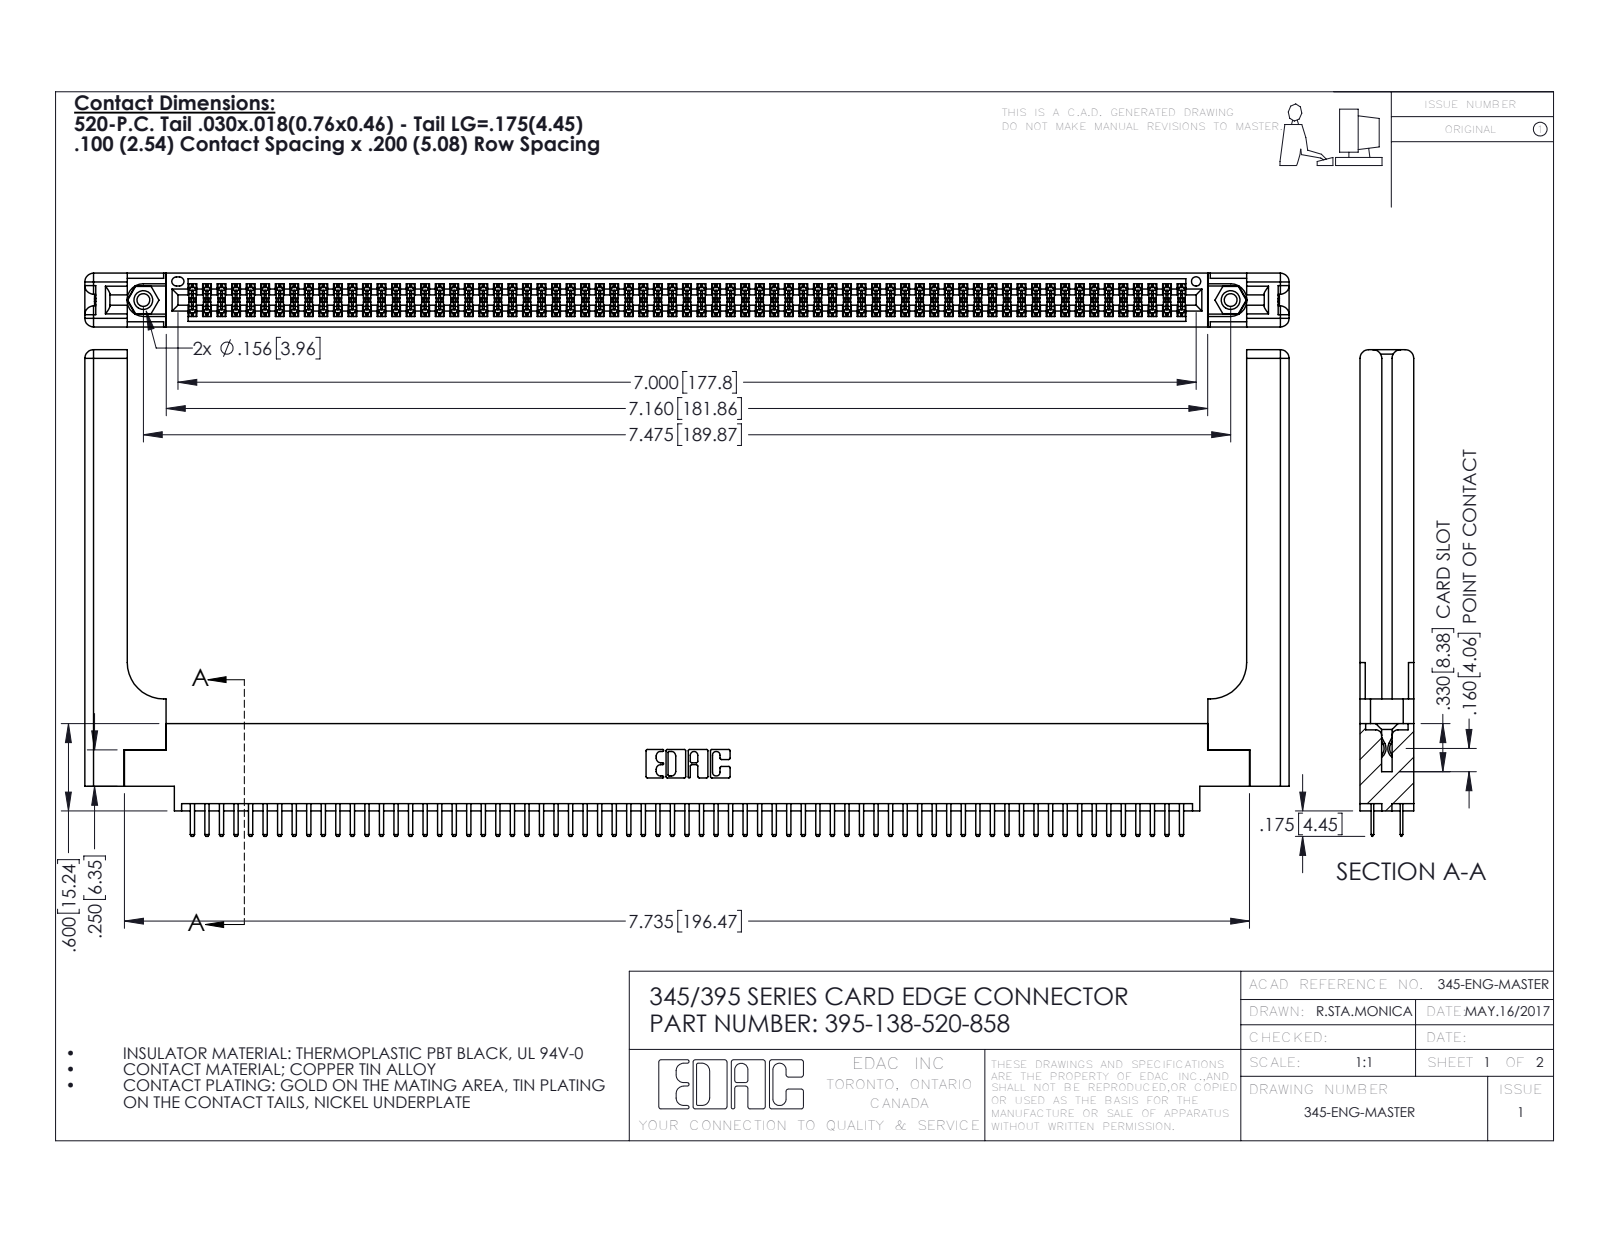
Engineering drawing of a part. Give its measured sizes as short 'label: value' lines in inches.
name: 345-292-001_345-293-120; 345-220-058_345-220-058; 345-250-001_345-250-001-102; 345 Part_0.170 Offset - 0.156 Dia-TH (+1 more)
written by: SolidWorks 2016 (CONFIG_CONTROL_DESIGN)
unit: in
bodies: 143 solids, 7838 faces (5062 planar, 2716 cylindrical, 60 other)
size: 8.279 × 3.345 × 0.37
volume: 1.768 in³; area: 55.65 in²
holes: 2× ⌀0.089, 2× ⌀0.125, 2× ⌀0.156, 1× ⌀0.064
bosses: 2× ⌀0.155
rounds: 207× R0.006, 142× R0.01, 22× R0.01, 16× R0.06, 6× R0.007, 6× R0.031, 3× R0.026, 2× R0.014
face distances: 0.072, 0.298, 0.37, 0.2, 0.098, 0.272, 0.025, 0.225, 0.022, 0.175
hole spacings: 0.27, 7.239, 7.475
